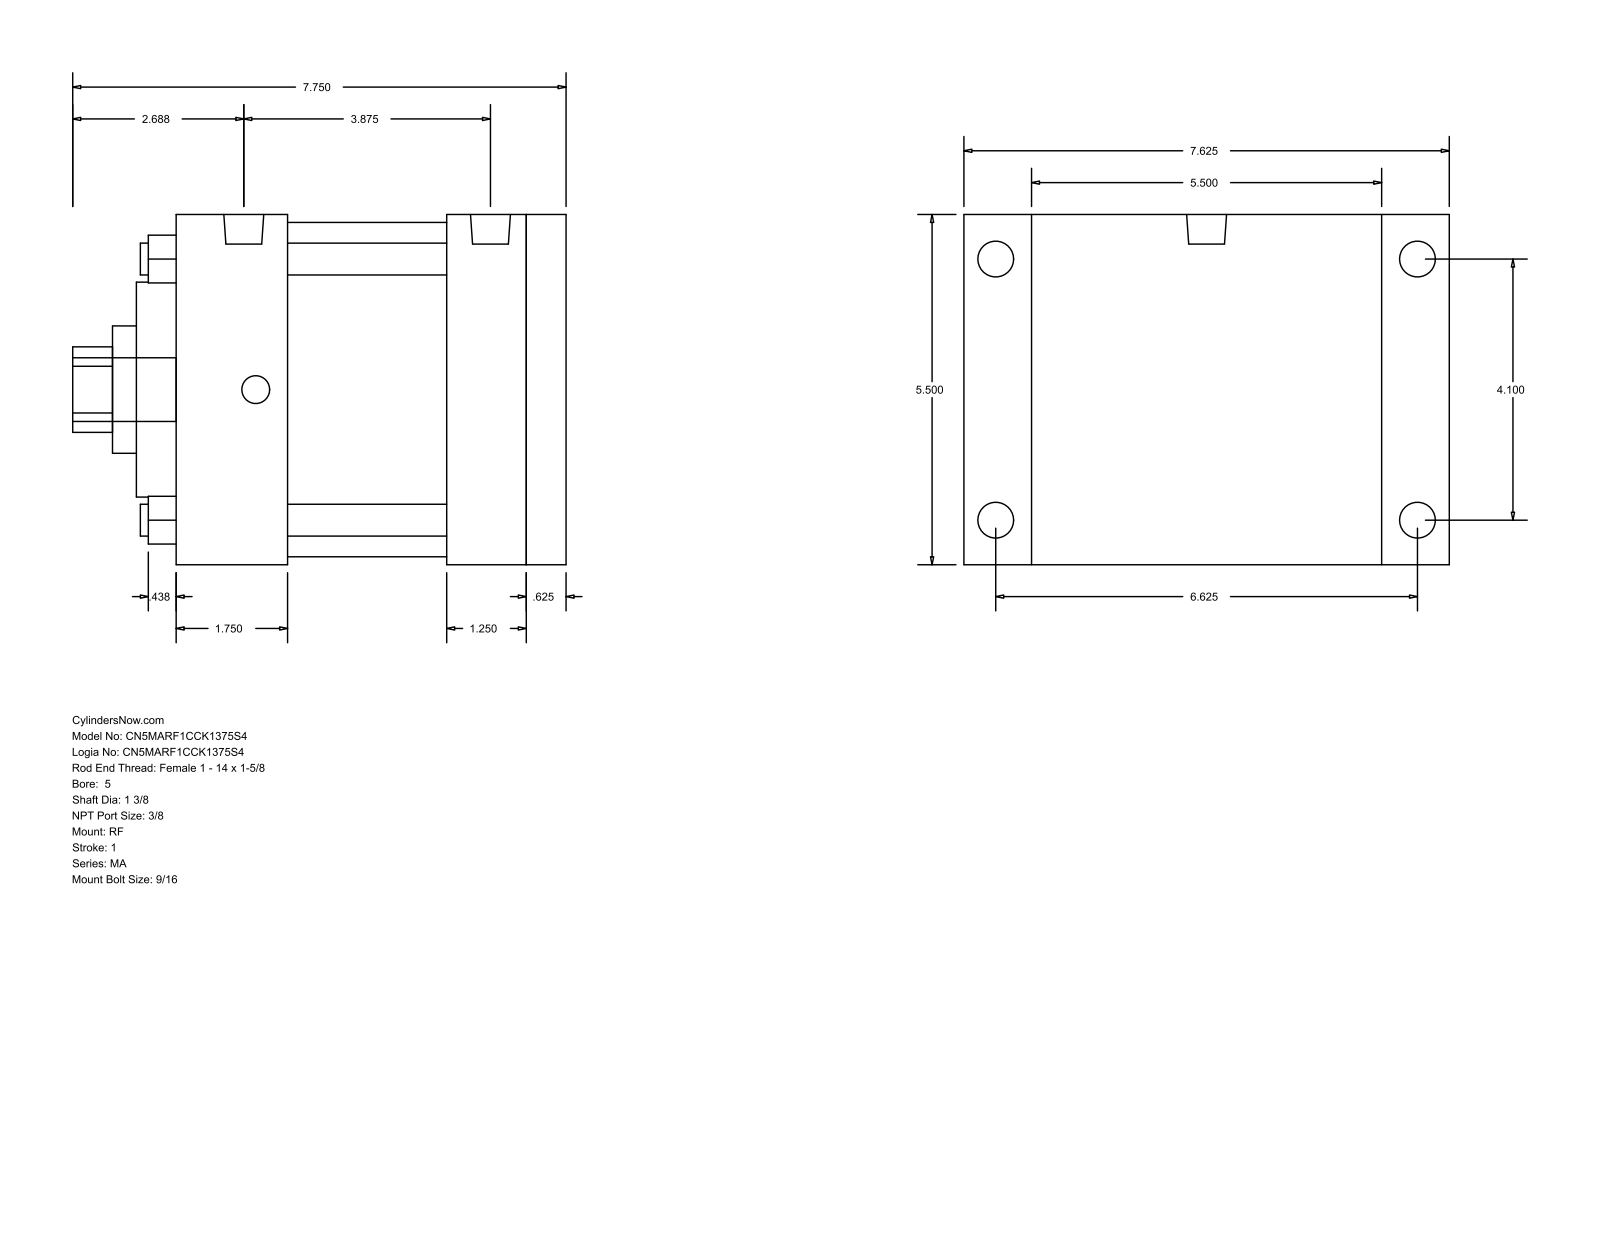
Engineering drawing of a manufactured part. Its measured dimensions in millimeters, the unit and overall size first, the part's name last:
Units: millimetres
Overall size (bounding box): 196.85 × 193.68 × 139.7
Round holes (diameter × count): ⌀12.7 ×4, ⌀34.92 ×1, ⌀50.8 ×1, ⌀85.72 ×1, ⌀133.35 ×1
Round bosses / shafts (diameter × count): ⌀14.29 ×4, ⌀11.11 ×4, ⌀15.93 ×2, ⌀25.4 ×1
Partial cylindrical surfaces — rounded edges, fillets, slot ends (radius × count): R17.06 ×1
Main face-to-face distances: 139.7, 155.58, 15.88, 111.13, 166.69, 44.45, 95.25, 107.95, 63.5, 31.75
Hole centre spacings: 73.64, 104.14, 147.28
Bodies: 0 solids, 94 faces (65 planar, 29 cylindrical, 0 other)
Part name (STEP PRODUCT): MA_RF__0500_1.375
STEP written by: GSSL Pune (CONFIG_CONTROL_DESIGN)
